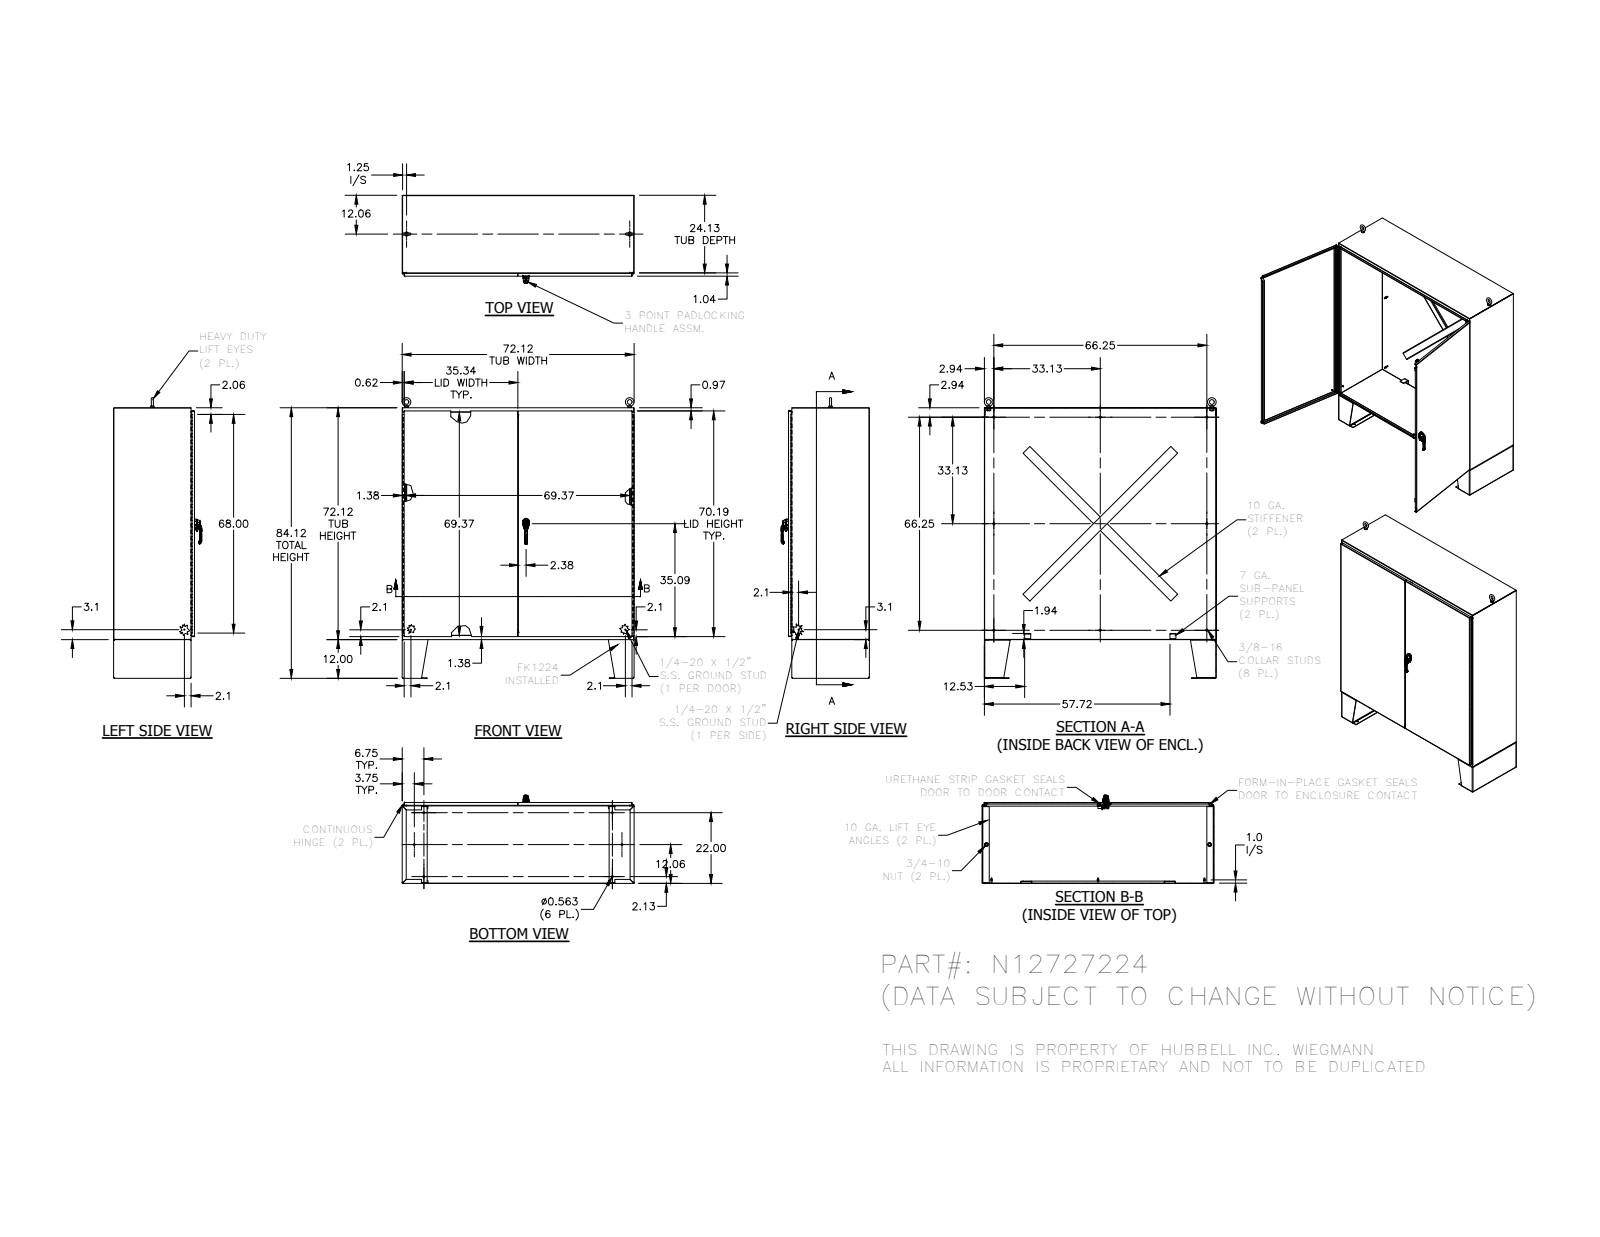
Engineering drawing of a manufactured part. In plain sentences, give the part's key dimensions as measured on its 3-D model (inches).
The part is named "N12727224". Its 3-D file was written by "SolidWorks 2018 (AUTOMOTIVE_DESIGN)". It is 76 solids with 2596 faces: 1528 planar, 768 cylindrical and 300 other. Overall it measures 87.248 by 78.798 by 27.338 inches. Its volume is 2 089 cubic inches and its surface area 42 413 square inches. Round holes: 18 of diameter 0.563, 8 of diameter 0.277, 4 of diameter 0.2, 3 of diameter 0.125, 3 of diameter 0.28, 2 of diameter 0.241, 2 of diameter 0.25, 2 of diameter 0.252, 2 of diameter 0.4, 2 of diameter 0.45, 2 of diameter 0.642, 2 of diameter 0.813. Round bosses or shafts: 8 of diameter 0.33, 5 of diameter 0.625, 5 of diameter 0.25, 3 of diameter 0.625, 3 of diameter 0.337, 2 of diameter 1.25, 2 of diameter 1.12, 2 of diameter 1. Partial cylindrical surfaces (rounded edges, fillets, slot ends): 24 of radius 0.031, 23 of radius 0.094, 22 of radius 0.219, 18 of radius 0.05, 16 of radius 0.025, 15 of radius 0.125, 13 of radius 0.03, 8 of radius 0.067. The main face-to-face distances are 0.094, 25.067, 72.031, 24.973, 25.16, 72.125, 71.938, 0.125, 0.125, 0.031. The hole center spacings are 2.041, 5, 10.38, 11.313, 22.75, 23.293, 58.393, 62.144.
